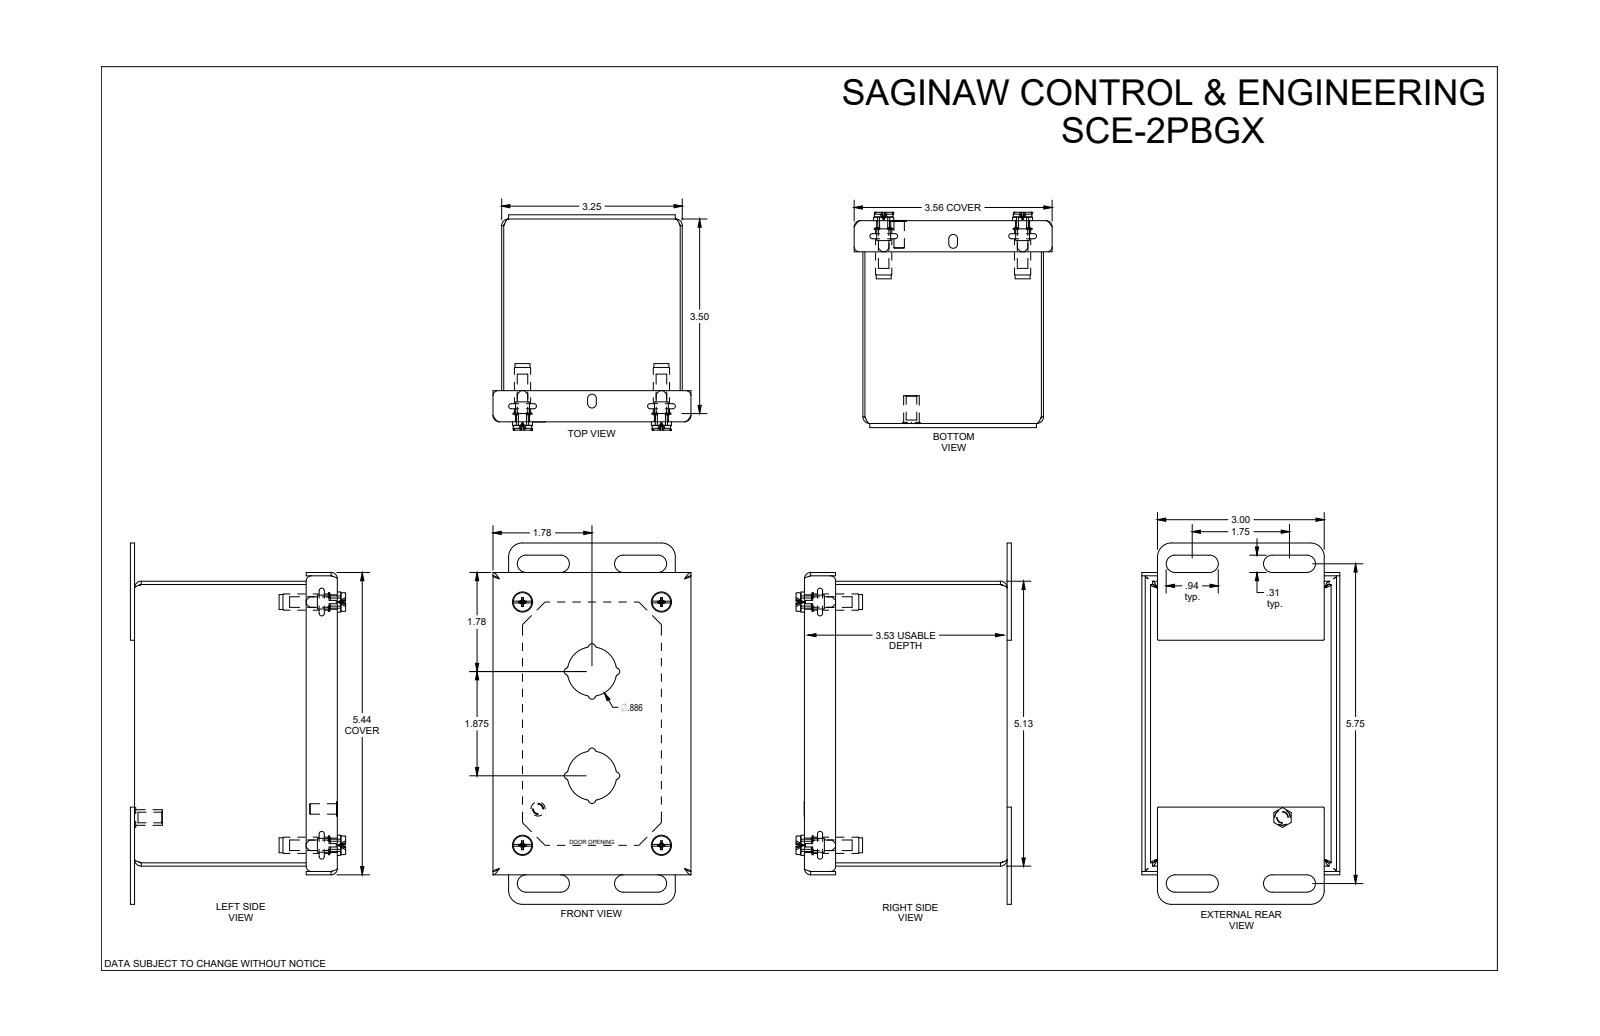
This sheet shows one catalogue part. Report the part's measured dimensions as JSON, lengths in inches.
{"part_name": "SCE-2PBGX", "step_written_by": "SolidWorks 2021 (AUTOMOTIVE_DESIGN)", "units": "inches", "bodies": {"solids": 15, "faces": 449, "planar": 162, "cylindrical": 211, "other": 76}, "overall_size": [6.5, 3.786, 3.562], "volume_in3": 7.494, "surface_area_in2": 249.9, "round_holes": [[0.19, 5], [0.22, 4], [0.25, 4], [0.266, 4], [0.317, 4]], "round_bosses_or_shafts": [[0.362, 4], [0.34, 4], [0.292, 4], [0.27, 4], [0.26, 4], [0.28, 1], [0.256, 1], [0.188, 1]], "partial_cylinders_radius": [[0.06, 20], [0.04, 16], [0.015, 8], [0.062, 8], [0.115, 8], [0.156, 8], [0.245, 8], [0.02, 4]], "face_to_face_distances": [0.06, 3.588, 3.19, 5.065, 3.648, 3.13, 3.25, 3.528, 0.156, 5.125], "hole_center_spacings": [4.375, 5.039, 2.5, 2.5, 5.032, 0.7, 0.707, 2.061]}
